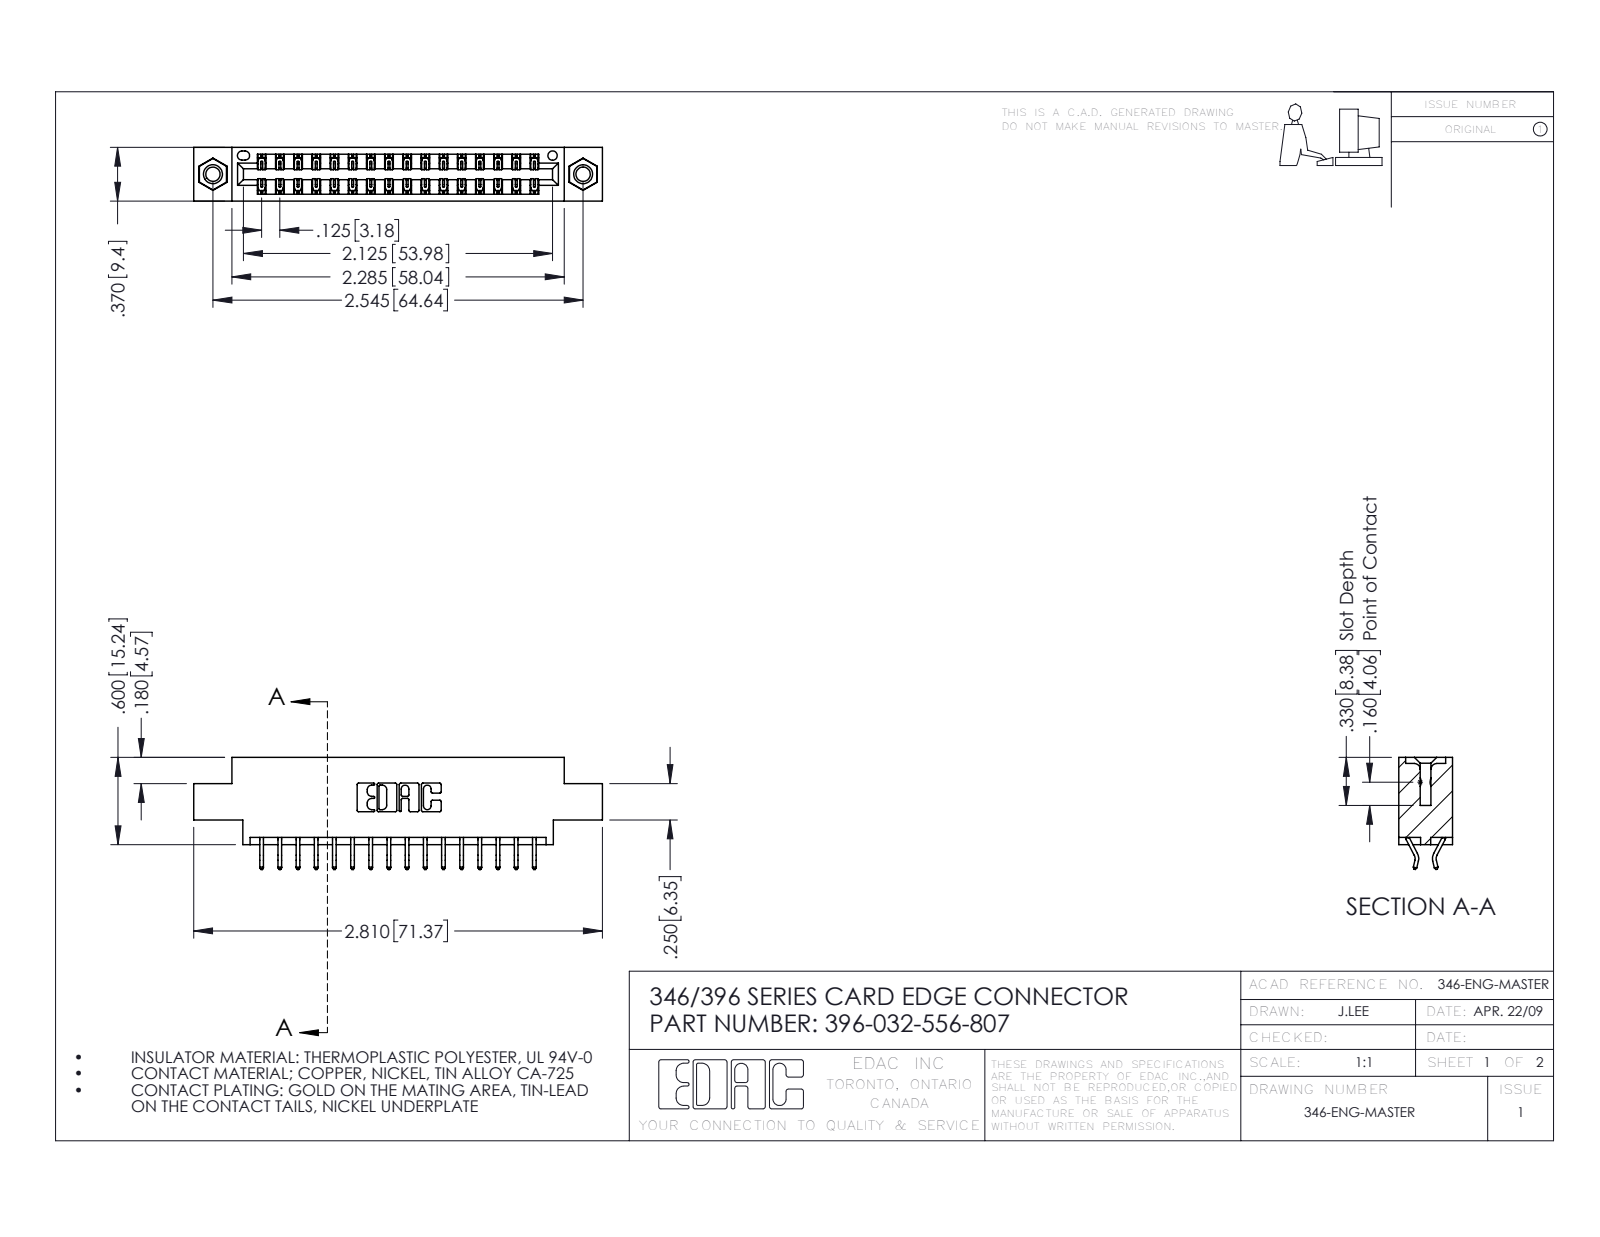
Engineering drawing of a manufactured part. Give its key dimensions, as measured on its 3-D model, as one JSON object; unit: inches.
{"part_name": "345-292-001_556 Tail; 346 Part_0.170 Offset - 0.156 Dia-TI; 396-032-556-807; 345-250-001_345-250-005-103", "step_written_by": "SolidWorks 2016 (CONFIG_CONTROL_DESIGN)", "units": "inches", "bodies": {"solids": 35, "faces": 2042, "planar": 1360, "cylindrical": 666, "other": 16}, "overall_size": [2.81, 0.77, 0.37], "volume_in3": 0.402, "surface_area_in2": 13.69, "round_holes": [[0.098, 2], [0.125, 2], [0.156, 2], [0.064, 1]], "round_bosses_or_shafts": [[0.155, 2]], "partial_cylinders_radius": [[0.006, 48], [0.01, 22], [0.007, 6], [0.031, 6], [0.026, 3], [0.01, 2], [0.014, 2], [0.022, 2]], "face_to_face_distances": [0.048, 0.322, 0.37, 0.25, 0.025, 0.072, 0.298, 0.222, 0.275, 0.148], "hole_center_spacings": [0.246, 2.338, 2.545]}
